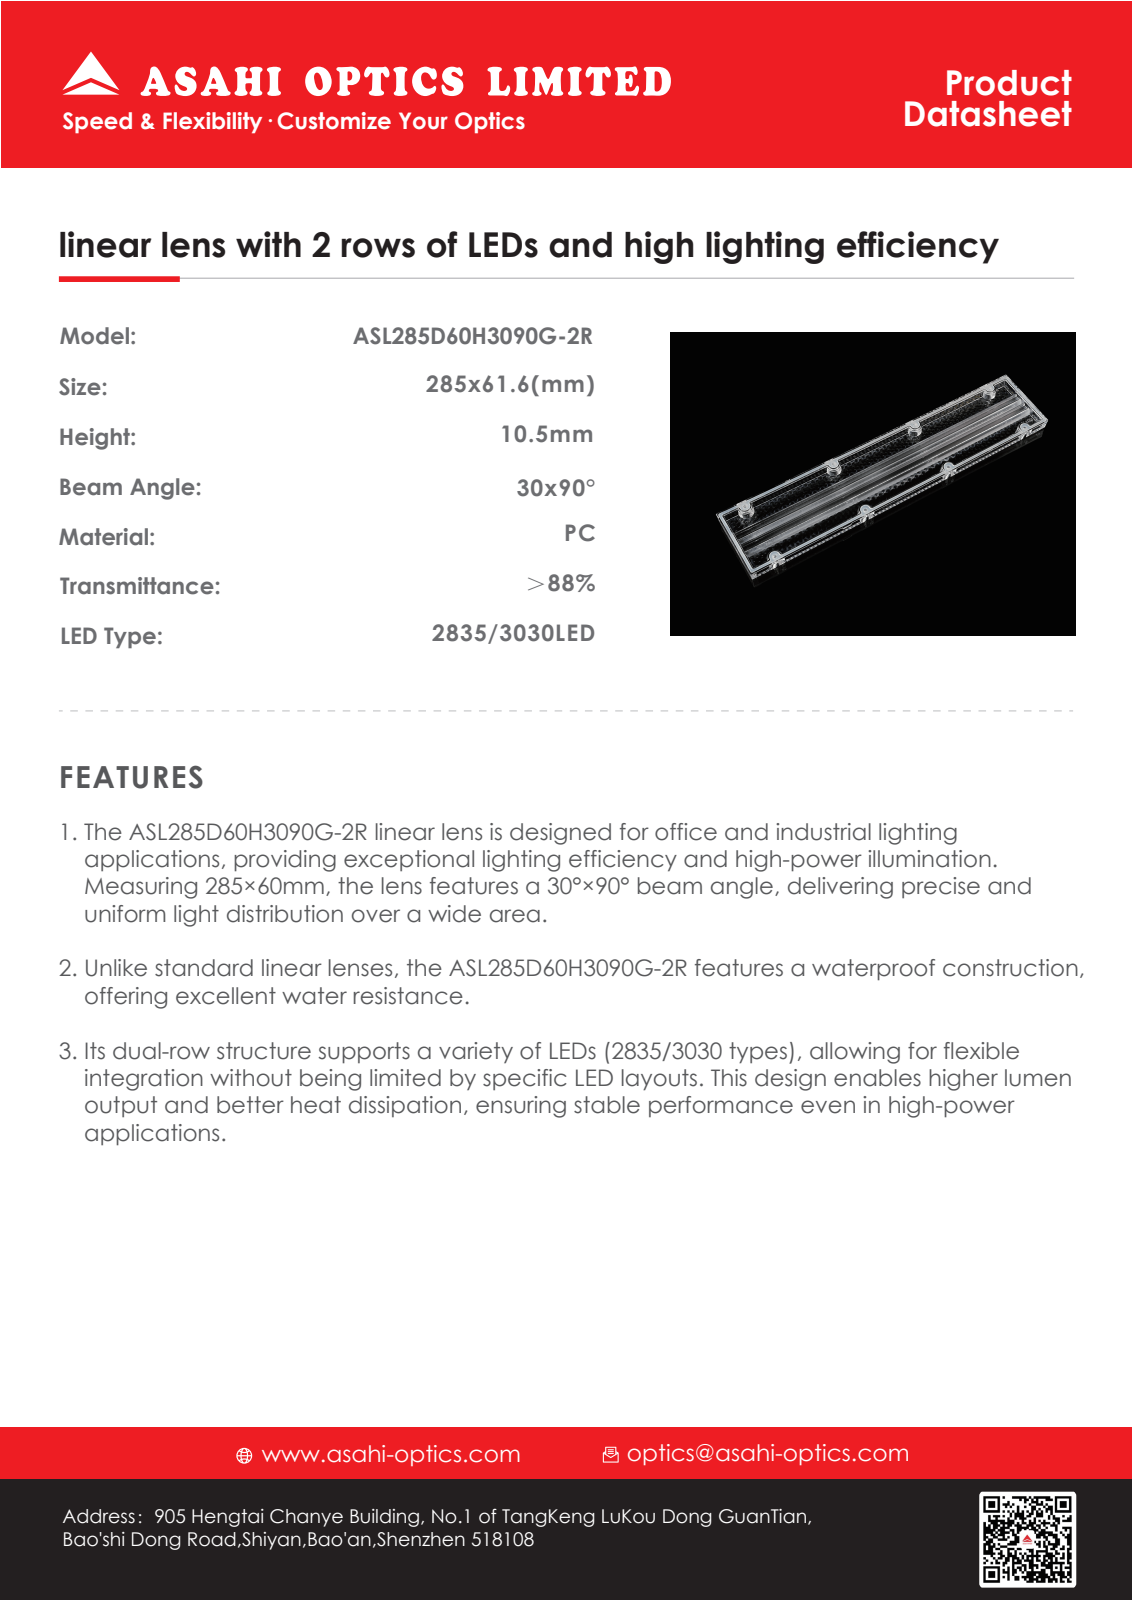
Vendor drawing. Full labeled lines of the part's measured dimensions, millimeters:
Part name (STEP PRODUCT): Admi9158F9A0y529
STEP written by: SIEMENS PLM Software NX 10.0 (AP203_CONFIGURATION_CONTROLLED_3D_DESIGN_OF_MECHANICAL_PARTS_AND_ASSEMBLIES_MIM_LF)
Units: millimetres
Bodies: 3 solids, 4663 faces (4180 planar, 219 cylindrical, 264 other)
Overall size (bounding box): 285 × 61 × 11
Volume: 99 957 mm³ · Surface area: 86 526 mm²
Round holes (diameter × count): ⌀3.2 ×8
Partial cylindrical surfaces — rounded edges, fillets, slot ends (radius × count): R1 ×66, R1.5 ×54, R0.3 ×40, R18 ×2, R4 ×1
Main face-to-face distances: 1.6, 10.5, 8.9, 4.5, 2.9, 6, 5.49, 2.5, 56.36, 2.3
Hole centre spacings: 80, 94.87, 51, 160, 167.93, 240, 245.36
